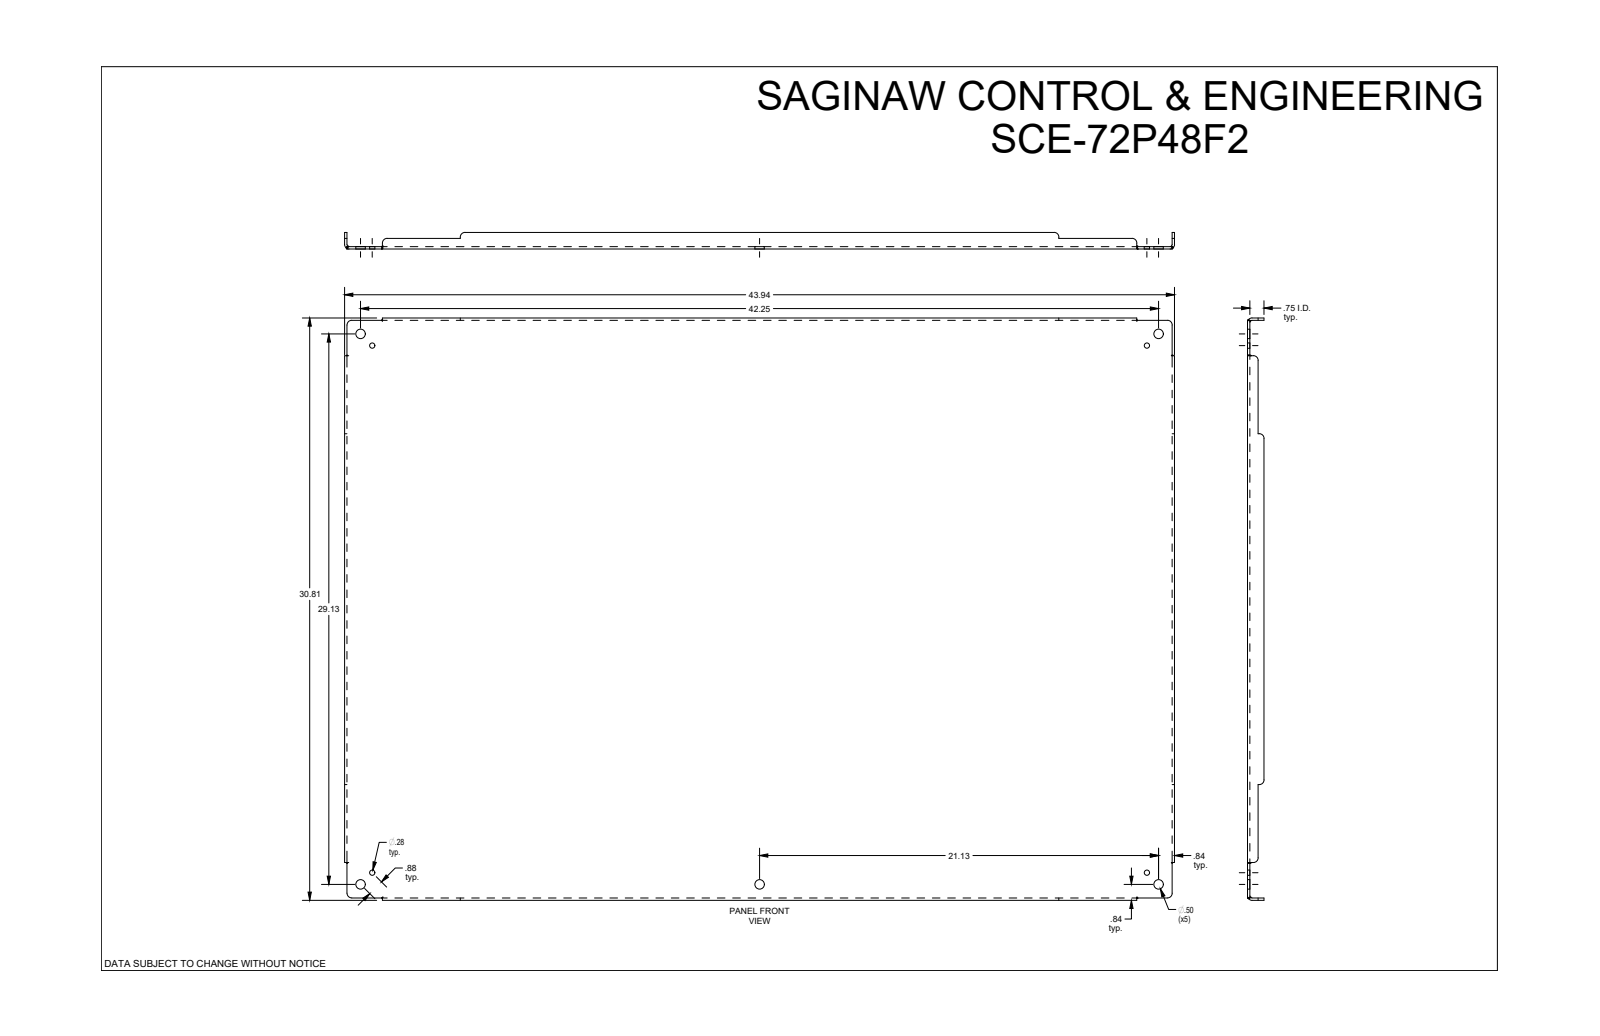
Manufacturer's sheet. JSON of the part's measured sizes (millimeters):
{"part_name": "SCE-72P48F2", "step_written_by": "SolidWorks 2019 (CONFIG_CONTROL_DESIGN)", "units": "millimeters", "bodies": {"solids": 1, "faces": 107, "planar": 46, "cylindrical": 37, "other": 24}, "overall_size": [1116, 782.7, 22.2], "volume_mm3": 2930000, "surface_area_mm2": 1859000, "round_holes": [[12.7, 5], [7.1, 4]], "partial_cylinders_radius": [[6.4, 12], [2.8, 4], [6, 4]], "face_to_face_distances": [3.2, 3.2, 779.4, 1112.9, 776.3, 782.7, 1109.6, 1116, 19.1, 22.2], "hole_center_spacings": [22.2, 724.2, 1057.6, 1281.6, 521.1, 536.6, 708.3, 739.8]}
